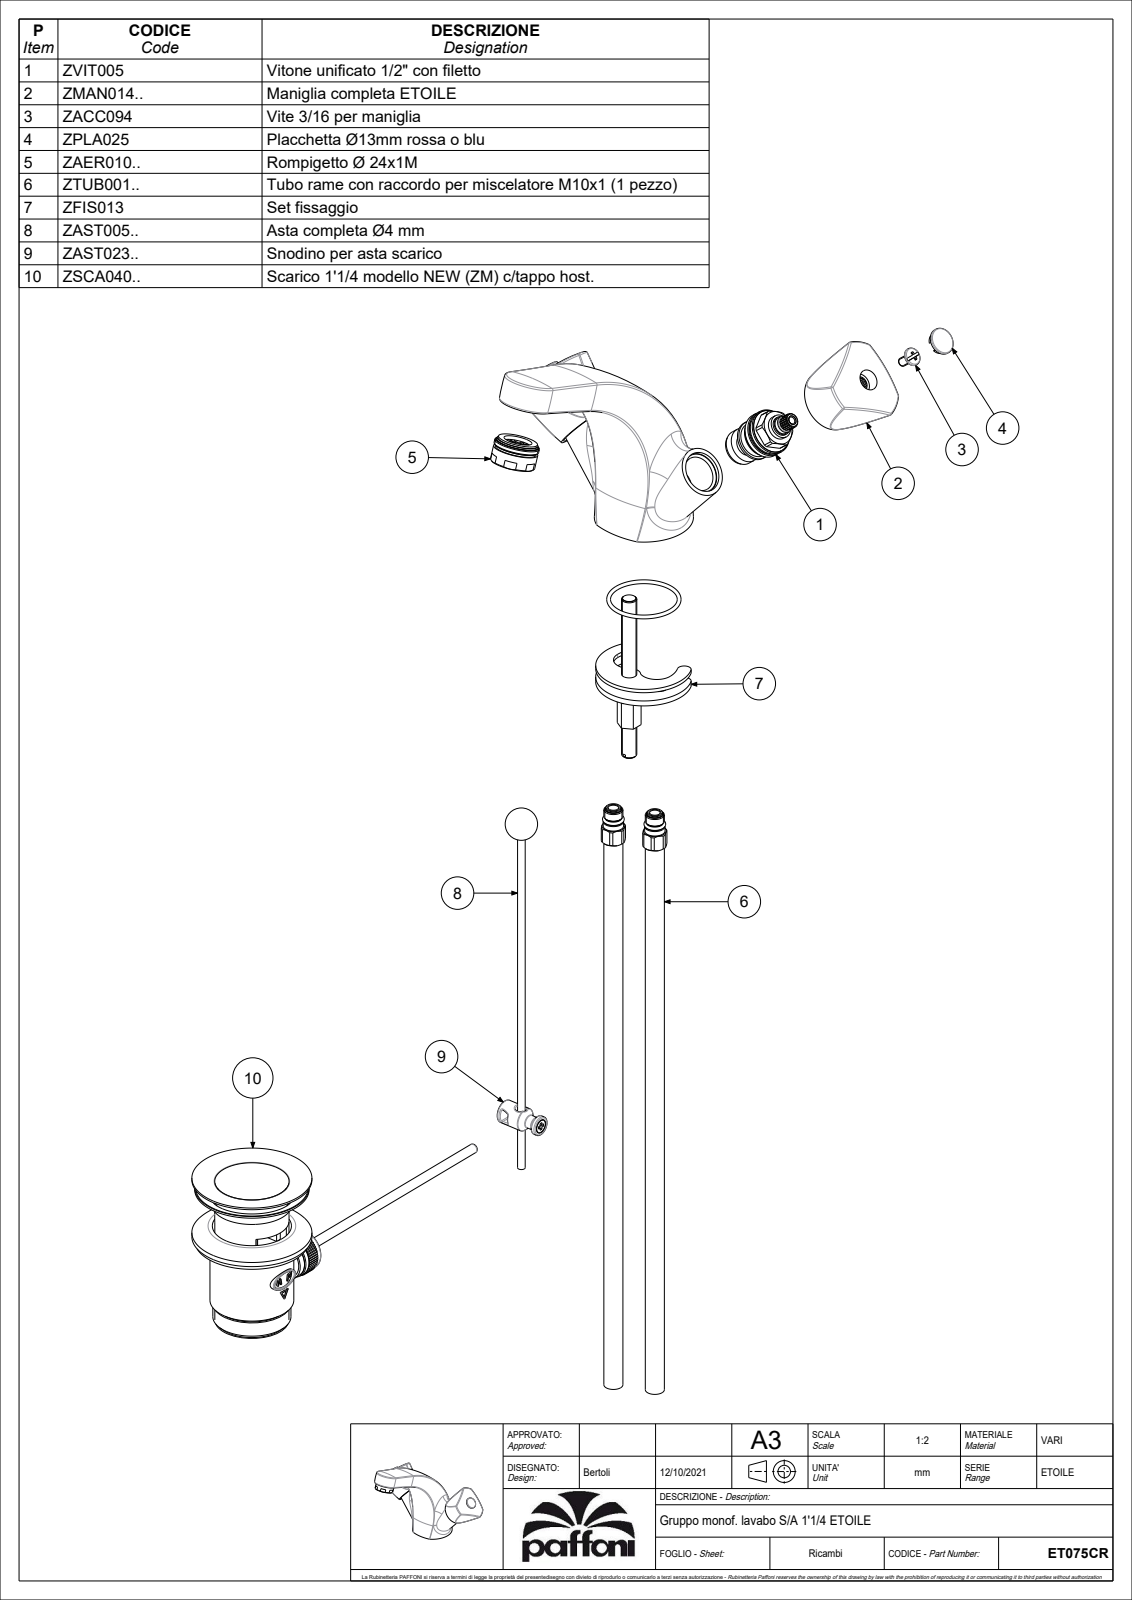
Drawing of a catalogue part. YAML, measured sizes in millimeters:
part_name: "ET075CR"
step_written_by: "CREO PARAMETRIC BY PTC INC, 2020044 (CONFIG_CONTROL_DESIGN)"
units: millimeters
bodies: {solids: 1, faces: 489, planar: 140, cylindrical: 125, other: 224}
overall_size: [154.04, 133.74, 128.34]
volume: 150472
surface_area: 75929
round_holes:
  - {diameter: 8, count: 2}
  - {diameter: 9, count: 2}
  - {diameter: 11, count: 2}
  - {diameter: 29.6, count: 2}
  - {diameter: 4.8, count: 1}
  - {diameter: 5.5, count: 1}
  - {diameter: 7, count: 1}
  - {diameter: 15, count: 1}
  - {diameter: 16, count: 1}
  - {diameter: 19, count: 1}
  - {diameter: 24.5, count: 1}
  - {diameter: 40, count: 1}
round_bosses_or_shafts:
  - {diameter: 24, count: 2}
  - {diameter: 22.5, count: 2}
  - {diameter: 18.6, count: 2}
  - {diameter: 17.3, count: 2}
  - {diameter: 14, count: 2}
  - {diameter: 12.5, count: 2}
  - {diameter: 11.5, count: 2}
  - {diameter: 9, count: 2}
partial_cylinders:
  - {radius: 1, count: 4}
  - {radius: 3, count: 2}
  - {radius: 5, count: 2}
  - {radius: 8, count: 2}
  - {radius: 10, count: 2}
  - {radius: 15, count: 2}
  - {radius: 3.4, count: 1}
  - {radius: 7.6, count: 1}
face_to_face_distances: [9, 6, 23, 12, 29, 1.5, 15, 40.81, 24, 46.81]
hole_center_spacings: [7.5, 11.72, 14.15, 9, 12, 15, 21]
